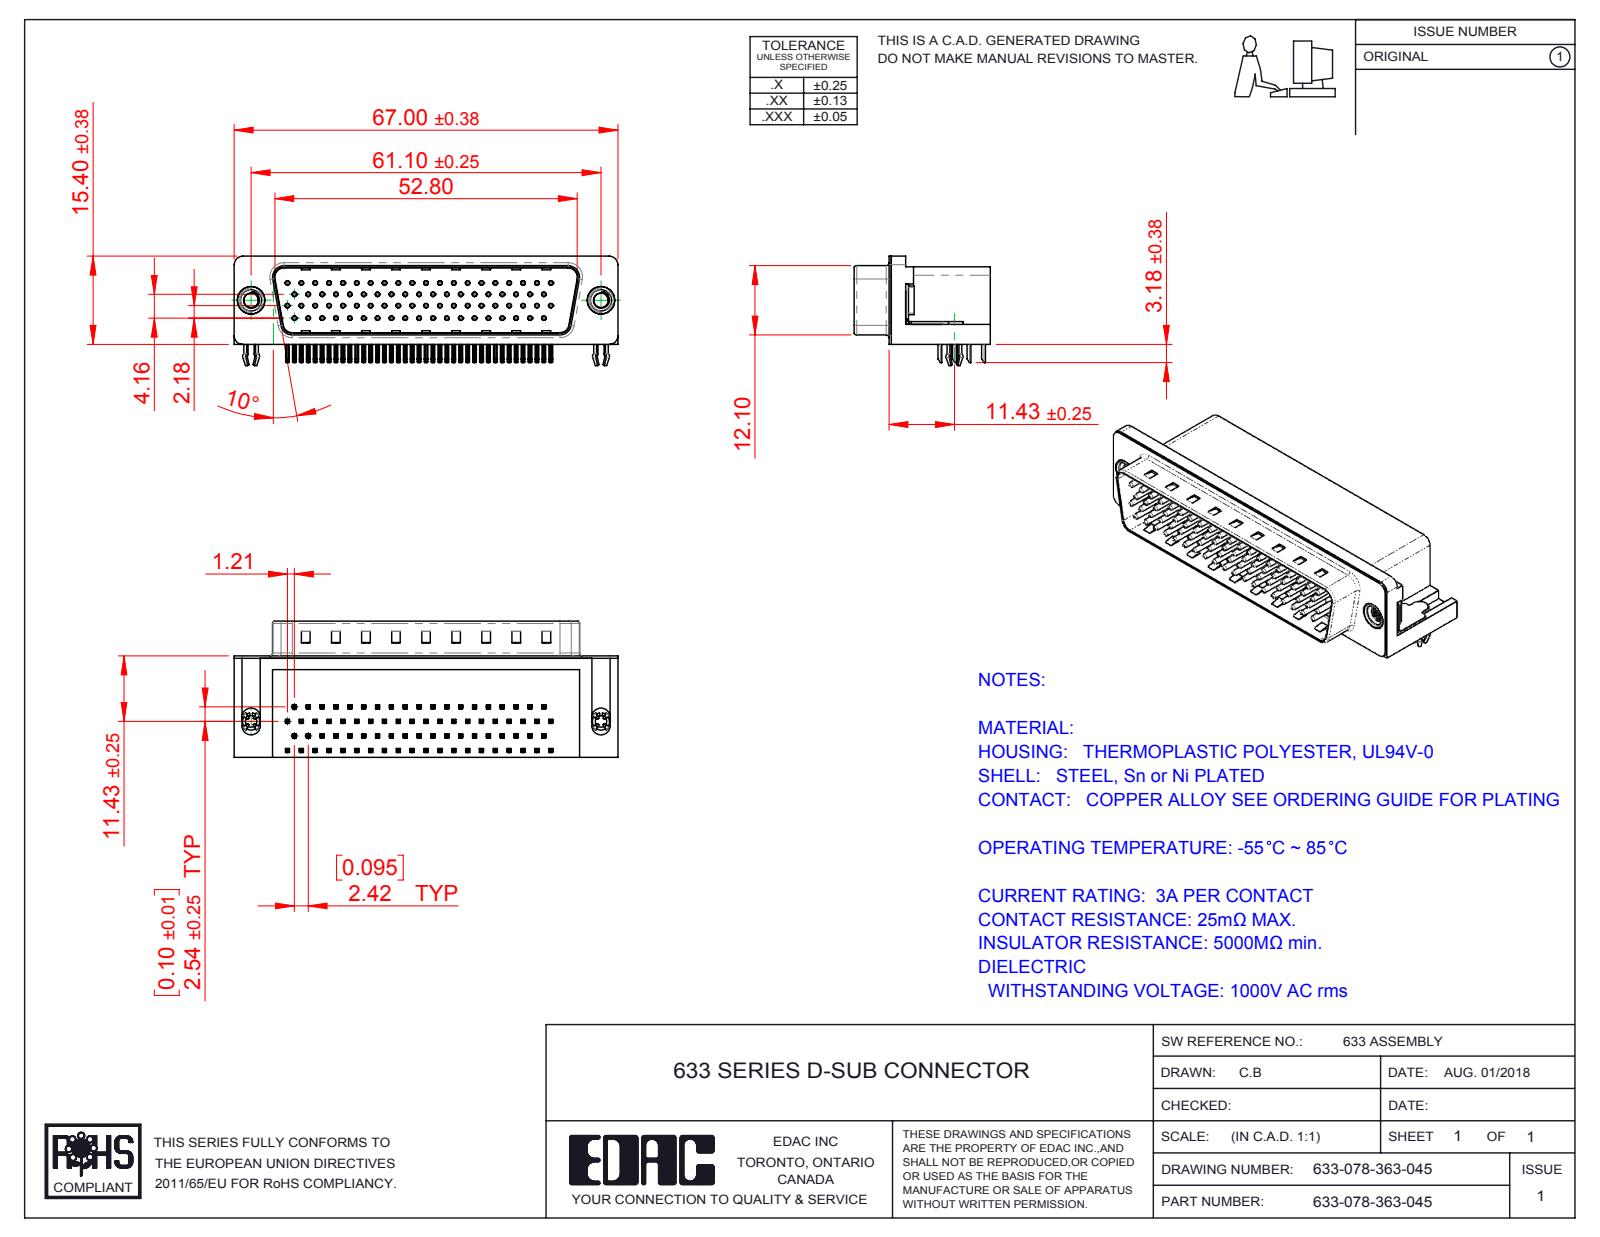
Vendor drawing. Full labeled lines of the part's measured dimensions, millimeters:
Part name (STEP PRODUCT): 633 M3 Threaded Rivet; 633 Housing_78 Contact; 633 4 Prong Board Lock_78 Contact; 633 Contact Top_78 Contact (+5 more)
STEP written by: SolidWorks 2016 (CONFIG_CONTROL_DESIGN)
Units: millimetres
Bodies: 84 solids, 6396 faces (4023 planar, 1788 cylindrical, 585 other)
Overall size (bounding box): 67 × 23.8 × 19.1
Volume: 14 617 mm³ · Surface area: 16 433 mm²
Round holes (diameter × count): ⌀0.35 ×78, ⌀0.8 ×78, ⌀2 ×2, ⌀2.5 ×2, ⌀4 ×2, ⌀4.8 ×2, ⌀5 ×2
Round bosses / shafts (diameter × count): ⌀0.75 ×78, ⌀4.9 ×2, ⌀4.75 ×2, ⌀3.9 ×2, ⌀3 ×2
Partial cylindrical surfaces — rounded edges, fillets, slot ends (radius × count): R0.25 ×324, R0.12 ×156, R1 ×16, R0.5 ×9, R1.6 ×8, R1.5 ×6, R0.45 ×4, R0.9 ×4
Main face-to-face distances: 0.4, 13.2, 17.3, 11.7, 13.35, 2.05, 13.75, 1.65, 1.85, 11.9
Hole centre spacings: 2.42, 4.84, 7.26, 9.68, 6.26, 7.13, 12.1, 8.62
